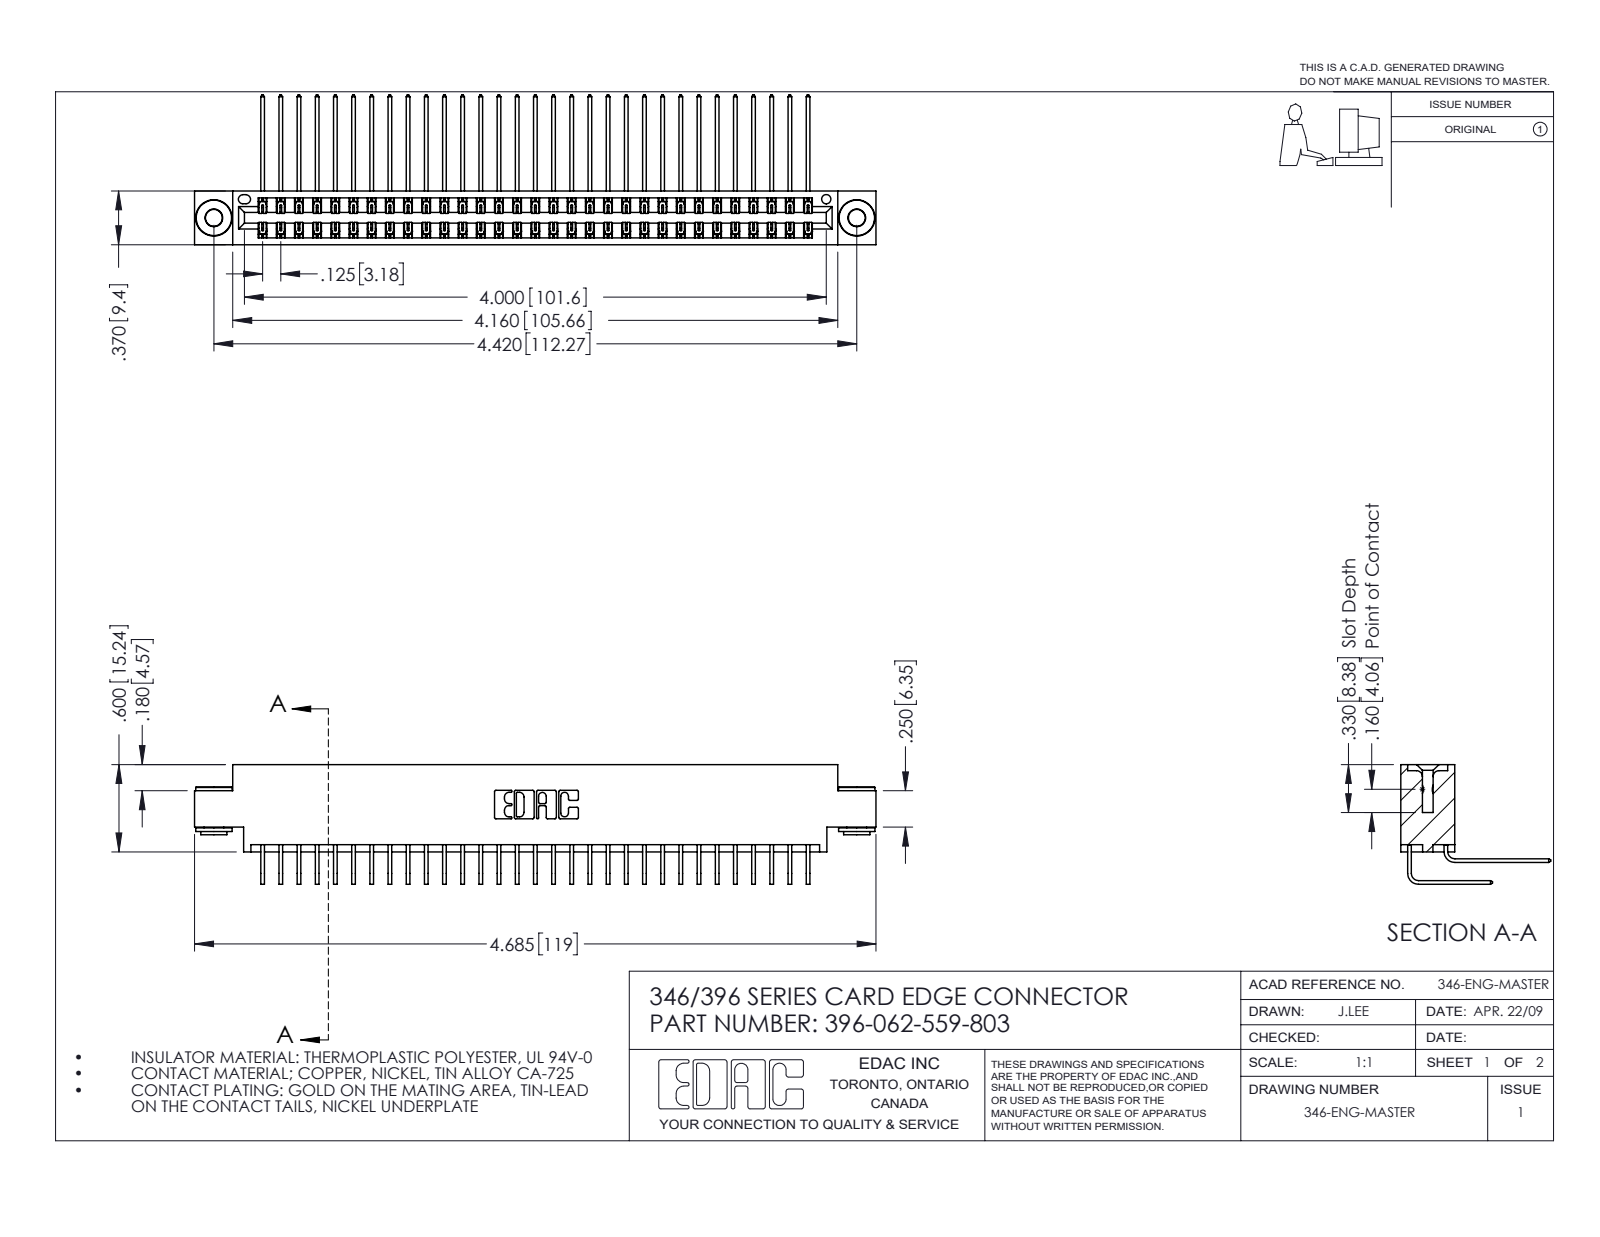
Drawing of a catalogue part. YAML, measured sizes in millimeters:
part_name: "396-062-559-803; 345-250-002_345-250-002-102; 346 Part_0.170 Offset - 0.156 Dia-TH; 345-292-001_559 Tail - 2 (+1 more)"
step_written_by: "SolidWorks 2016 (CONFIG_CONTROL_DESIGN)"
units: millimeters
bodies: {solids: 65, faces: 3512, planar: 2384, cylindrical: 1120, other: 8}
overall_size: [119, 26.2, 20.9]
volume: 11700
surface_area: 18080
round_holes:
  - {diameter: 2.9, count: 2}
  - {diameter: 4, count: 2}
  - {diameter: 1.6, count: 1}
round_bosses_or_shafts:
  - {diameter: 6.4, count: 2}
  - {diameter: 4.6, count: 2}
  - {diameter: 3.5, count: 2}
partial_cylinders:
  - {radius: 0.2, count: 93}
  - {radius: 0.3, count: 22}
  - {radius: 0.2, count: 6}
  - {radius: 0.8, count: 6}
  - {radius: 0.7, count: 3}
  - {radius: 0.4, count: 2}
  - {radius: 0.6, count: 2}
  - {radius: 0.6, count: 2}
face_to_face_distances: [1.2, 8.2, 0.6, 9.4, 6.4, 1.8, 7.6, 7, 3.8, 3.8]
hole_center_spacings: [6.2, 107, 112.3]
